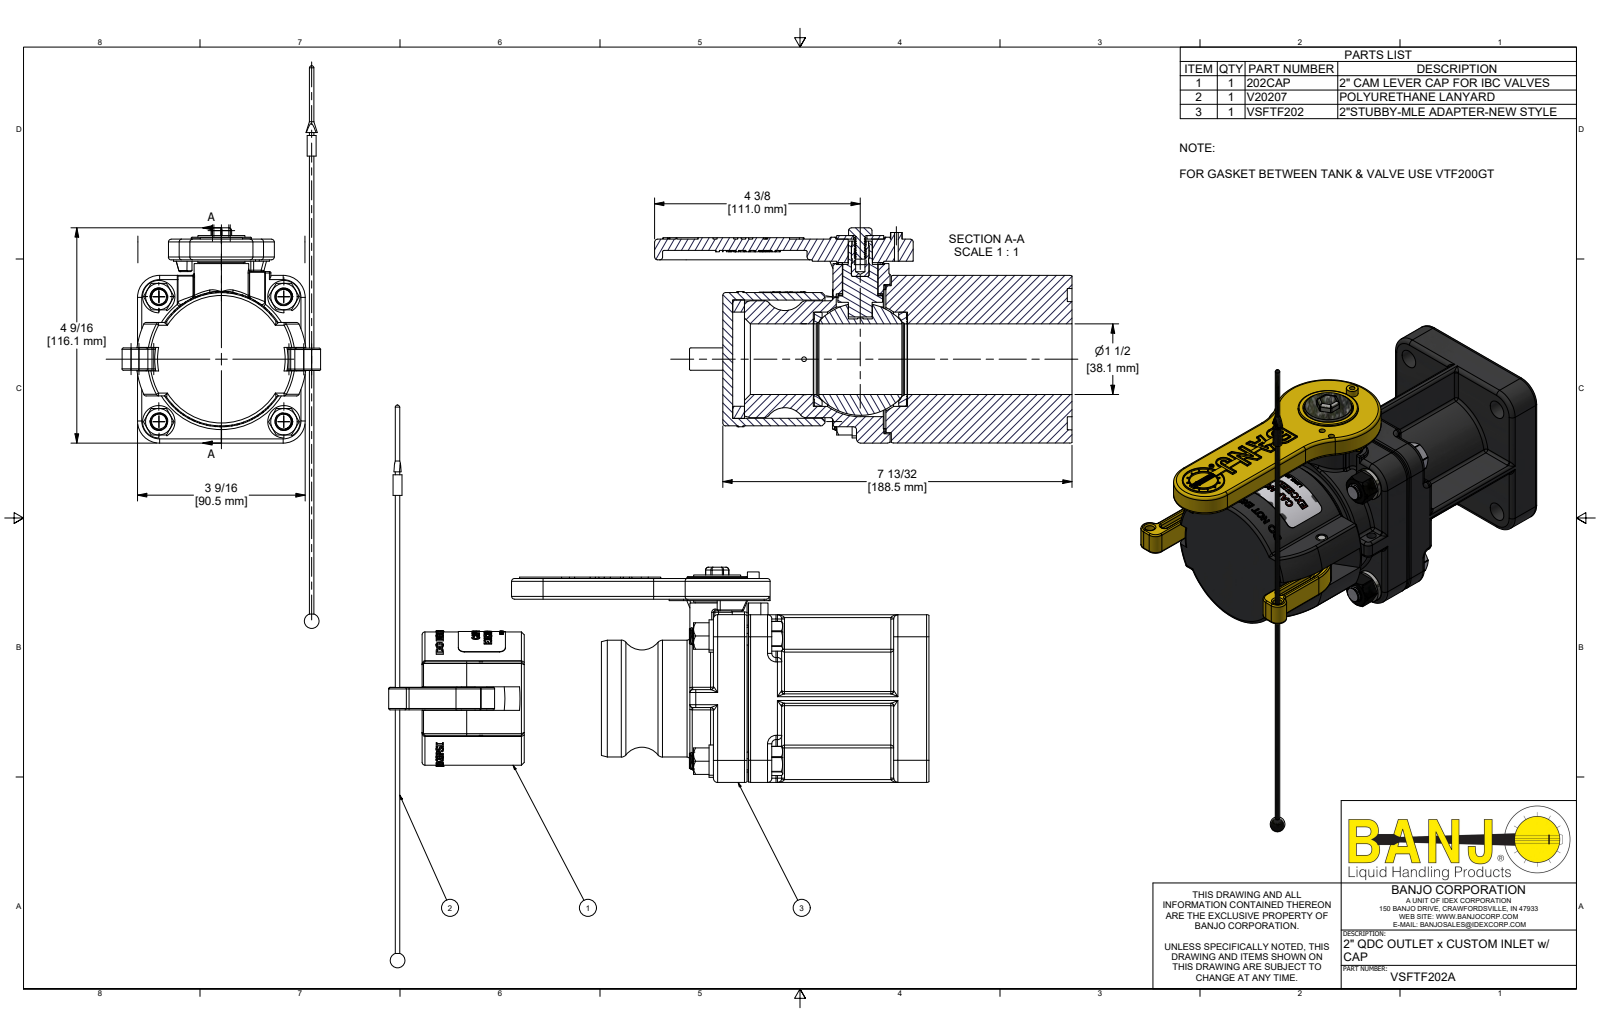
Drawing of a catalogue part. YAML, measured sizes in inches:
part_name: "VSFTF202A; VSFTF202; VSF20254; VSF20254X (+8 more)"
step_written_by: "Autodesk Inventor 2022 (AUTOMOTIVE_DESIGN)"
units: inches
bodies: {solids: 33, faces: 3712, planar: 1361, cylindrical: 908, other: 1443}
overall_size: [11.951, 8.87, 4.218]
volume: 44.68
surface_area: 366.9
round_holes:
  - {diameter: 0.375, count: 5}
  - {diameter: 0.2, count: 4}
  - {diameter: 0.307, count: 4}
  - {diameter: 0.385, count: 4}
  - {diameter: 0.406, count: 4}
  - {diameter: 0.41, count: 4}
  - {diameter: 0.1, count: 2}
  - {diameter: 0.13, count: 2}
  - {diameter: 0.253, count: 2}
  - {diameter: 0.256, count: 2}
  - {diameter: 0.076, count: 1}
  - {diameter: 0.118, count: 1}
round_bosses_or_shafts:
  - {diameter: 0.324, count: 60}
  - {diameter: 0.687, count: 4}
  - {diameter: 0.375, count: 4}
  - {diameter: 0.26, count: 2}
  - {diameter: 0.249, count: 2}
  - {diameter: 3.15, count: 1}
  - {diameter: 3.12, count: 1}
  - {diameter: 2.87, count: 1}
partial_cylinders:
  - {radius: 0.06, count: 77}
  - {radius: 0.03, count: 52}
  - {radius: 0.09, count: 44}
  - {radius: 0.015, count: 8}
  - {radius: 0.125, count: 8}
  - {radius: 0.162, count: 8}
  - {radius: 0.469, count: 8}
  - {radius: 0.19, count: 4}
face_to_face_distances: [1.88, 1.68, 3.83, 2.38, 0.2, 7.21, 0.75, 6.46, 7.42, 6.67]
hole_center_spacings: [2.654, 1.872, 1.88, 2.648, 2.659, 3.753, 1.393, 1.548]
